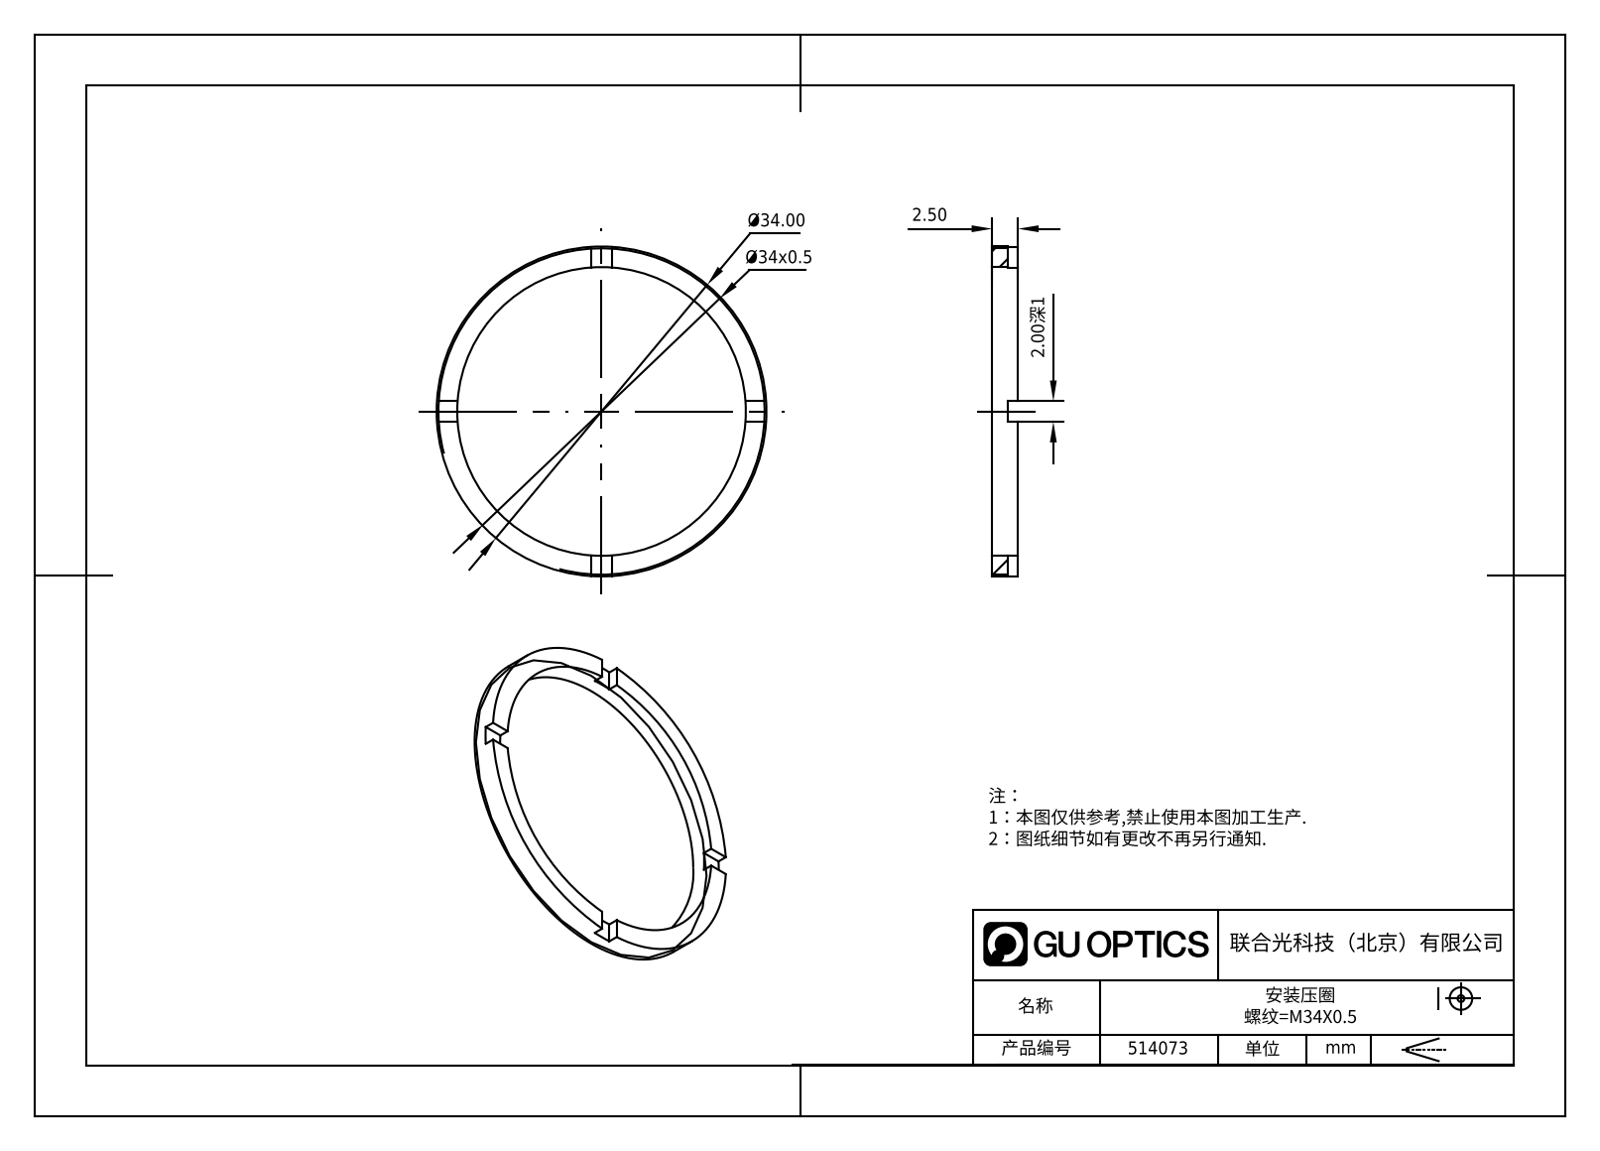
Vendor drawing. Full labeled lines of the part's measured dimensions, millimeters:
Part name (STEP PRODUCT): 514073
STEP written by: SolidWorks 2020 (CONFIG_CONTROL_DESIGN)
Units: millimetres
Bodies: 1 solid, 21 faces (17 planar, 4 cylindrical, 0 other)
Overall size (bounding box): 34 × 34 × 2.5
Volume: 487 mm³ · Surface area: 905 mm²
Round holes (diameter × count): ⌀30 ×1
Round bosses / shafts (diameter × count): ⌀34 ×1
Main face-to-face distances: 2.5, 1.5, 1, 2
